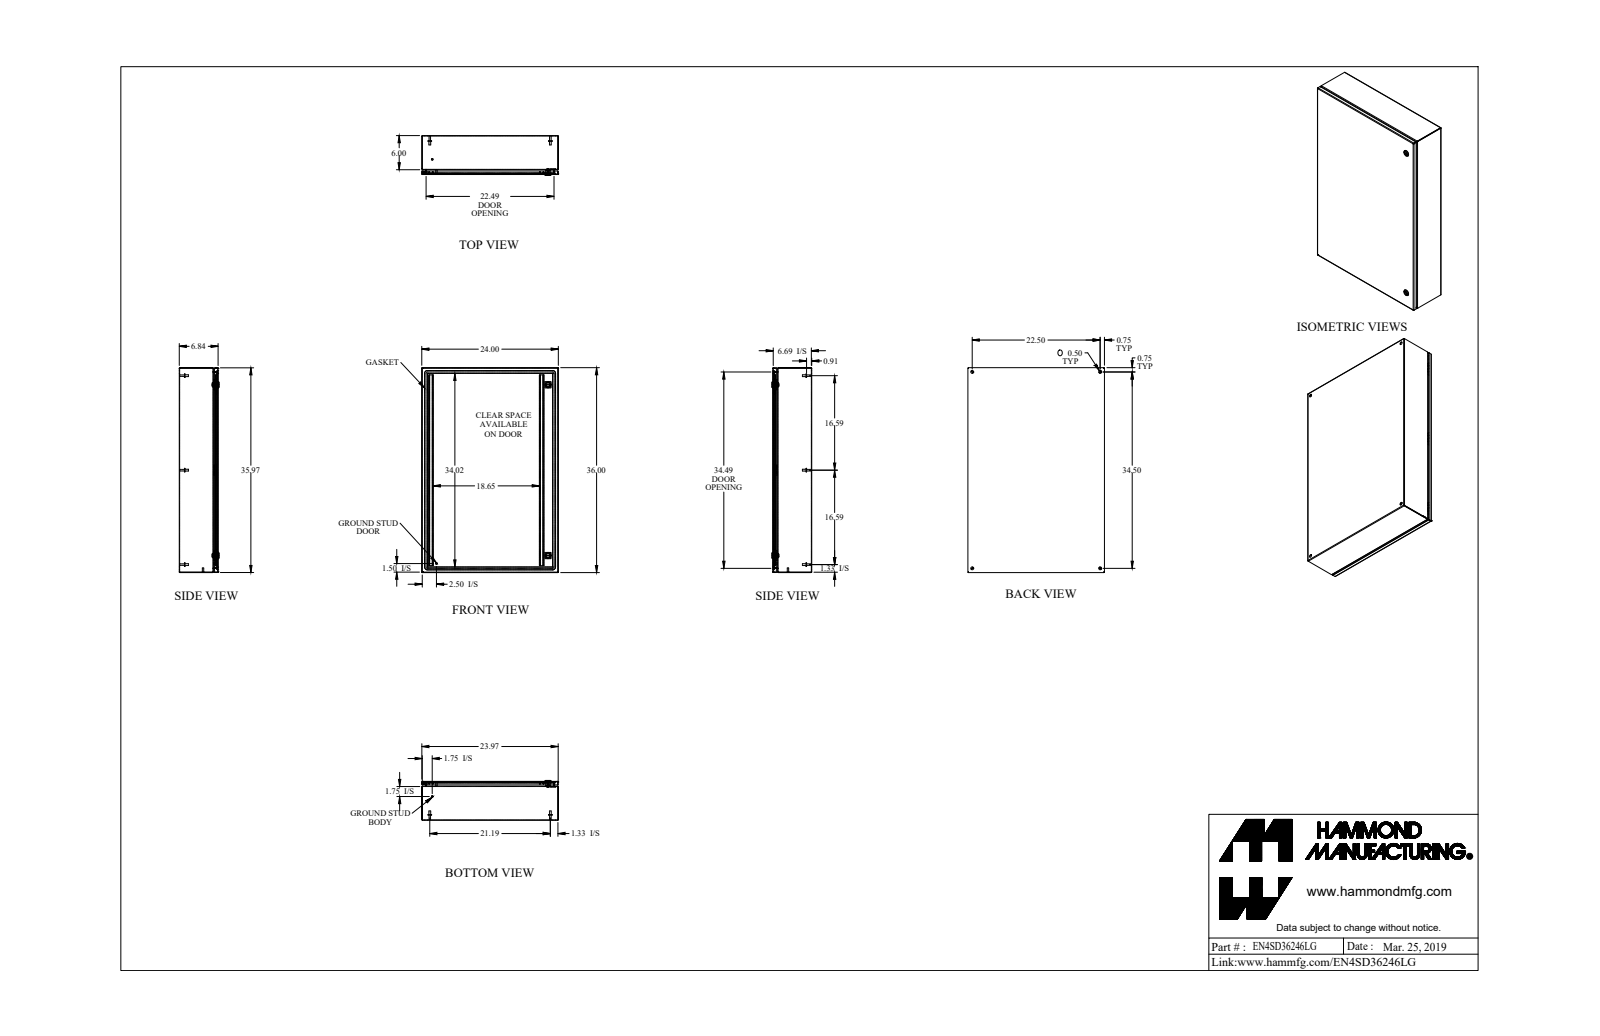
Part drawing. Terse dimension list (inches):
name: EN4SD36246LG_Default
written by: SolidWorks 2019 (CONFIG_CONTROL_DESIGN)
unit: in
bodies: 33 solids, 917 faces (430 planar, 307 cylindrical, 180 other)
size: 36 × 24 × 6.997
volume: 209.7 in³; area: 5 894 in²
holes: 4× ⌀0.5, 2× ⌀0.232, 2× ⌀0.625, 2× ⌀0.785, 1× ⌀0.172, 1× ⌀0.24, 1× ⌀0.242
bosses: 6× ⌀0.625, 6× ⌀0.313, 6× ⌀0.27, 2× ⌀1.1, 2× ⌀0.525, 2× ⌀0.281, 2× ⌀0.25, 1× ⌀0.455
rounds: 20× R0.036, 20× R0.108, 12× R0.043, 12× R0.081, 12× R0.382, 8× R19.003, 6× R0.006, 6× R0.062
face distances: 0.072, 6.765, 6.693, 6.837, 23.928, 35.928, 23.856, 24, 0.837, 5.928
hole spacings: 22.5, 34.5, 41.189, 2.493, 2.494, 21.545, 21.545, 29.999
